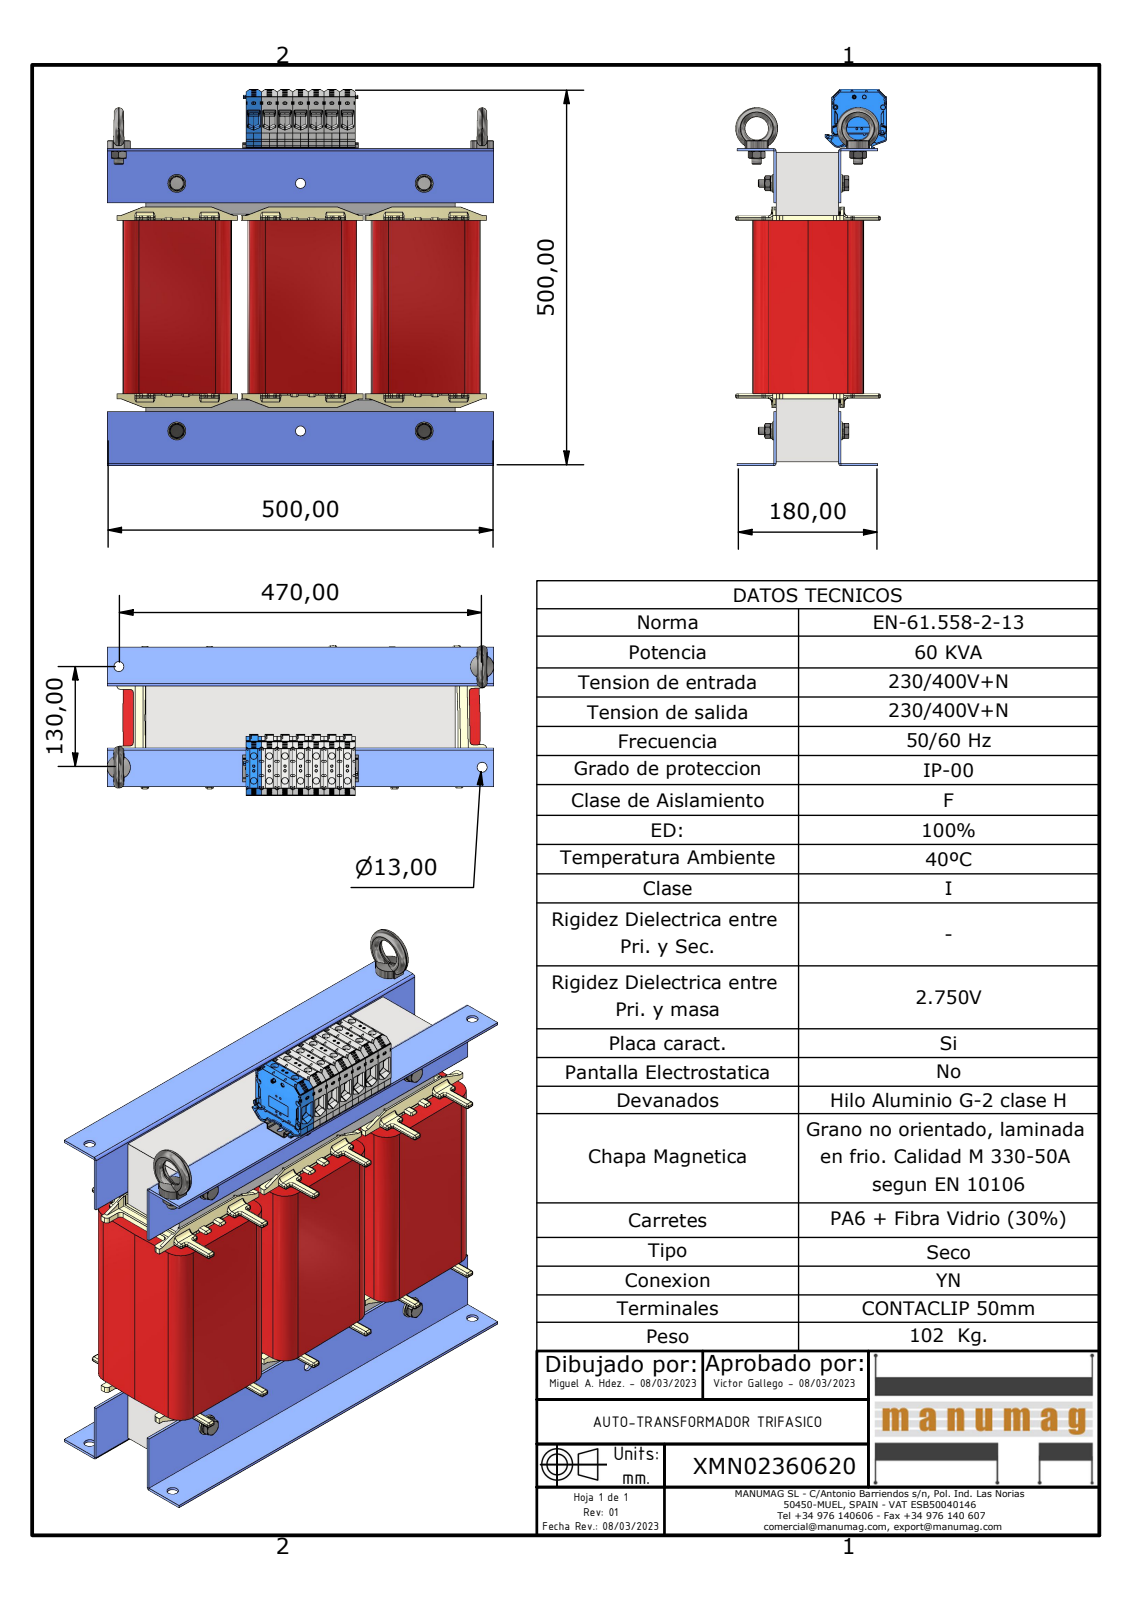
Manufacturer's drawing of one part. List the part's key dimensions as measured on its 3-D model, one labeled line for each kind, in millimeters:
Part name (STEP PRODUCT): XMN02360620; 3UI240 400 x 400 - 80; RC80 NT080; centrador M10 (+8 more)
STEP written by: Autodesk Inventor 2023 (AUTOMOTIVE_DESIGN)
Units: millimetres
Bodies: 65 solids, 11760 faces (6635 planar, 3991 cylindrical, 1134 other)
Overall size (bounding box): 500 × 486.7 × 193.93
Volume: 19 220 000 mm³ · Surface area: 2 495 000 mm²
Round holes (diameter × count): ⌀2.75 ×14, ⌀2.95 ×14, ⌀8.5 ×14, ⌀13 ×10, ⌀2.5 ×8, ⌀15 ×6, ⌀3.4 ×4, ⌀8.38 ×4, ⌀10 ×4, ⌀10.5 ×4, ⌀6.5 ×2, ⌀10.11 ×2
Round bosses / shafts (diameter × count): ⌀0.6 ×12, ⌀23 ×4, ⌀20 ×4, ⌀15.4 ×4, ⌀11.5 ×4, ⌀9.19 ×4, ⌀54 ×2, ⌀12 ×2
Partial cylindrical surfaces — rounded edges, fillets, slot ends (radius × count): R2 ×401, R0.3 ×325, R1 ×251, R1.9 ×60, R0.5 ×40, R0.81 ×33, R0.3 ×26, R0.49 ×24
Main face-to-face distances: 80, 3, 5.8, 83, 1.8, 22.96, 28.76, 407, 24.76, 4
Hole centre spacings: 20.2, 24.02, 27.73, 40.4, 42.44, 44.64, 60.6, 61.98
